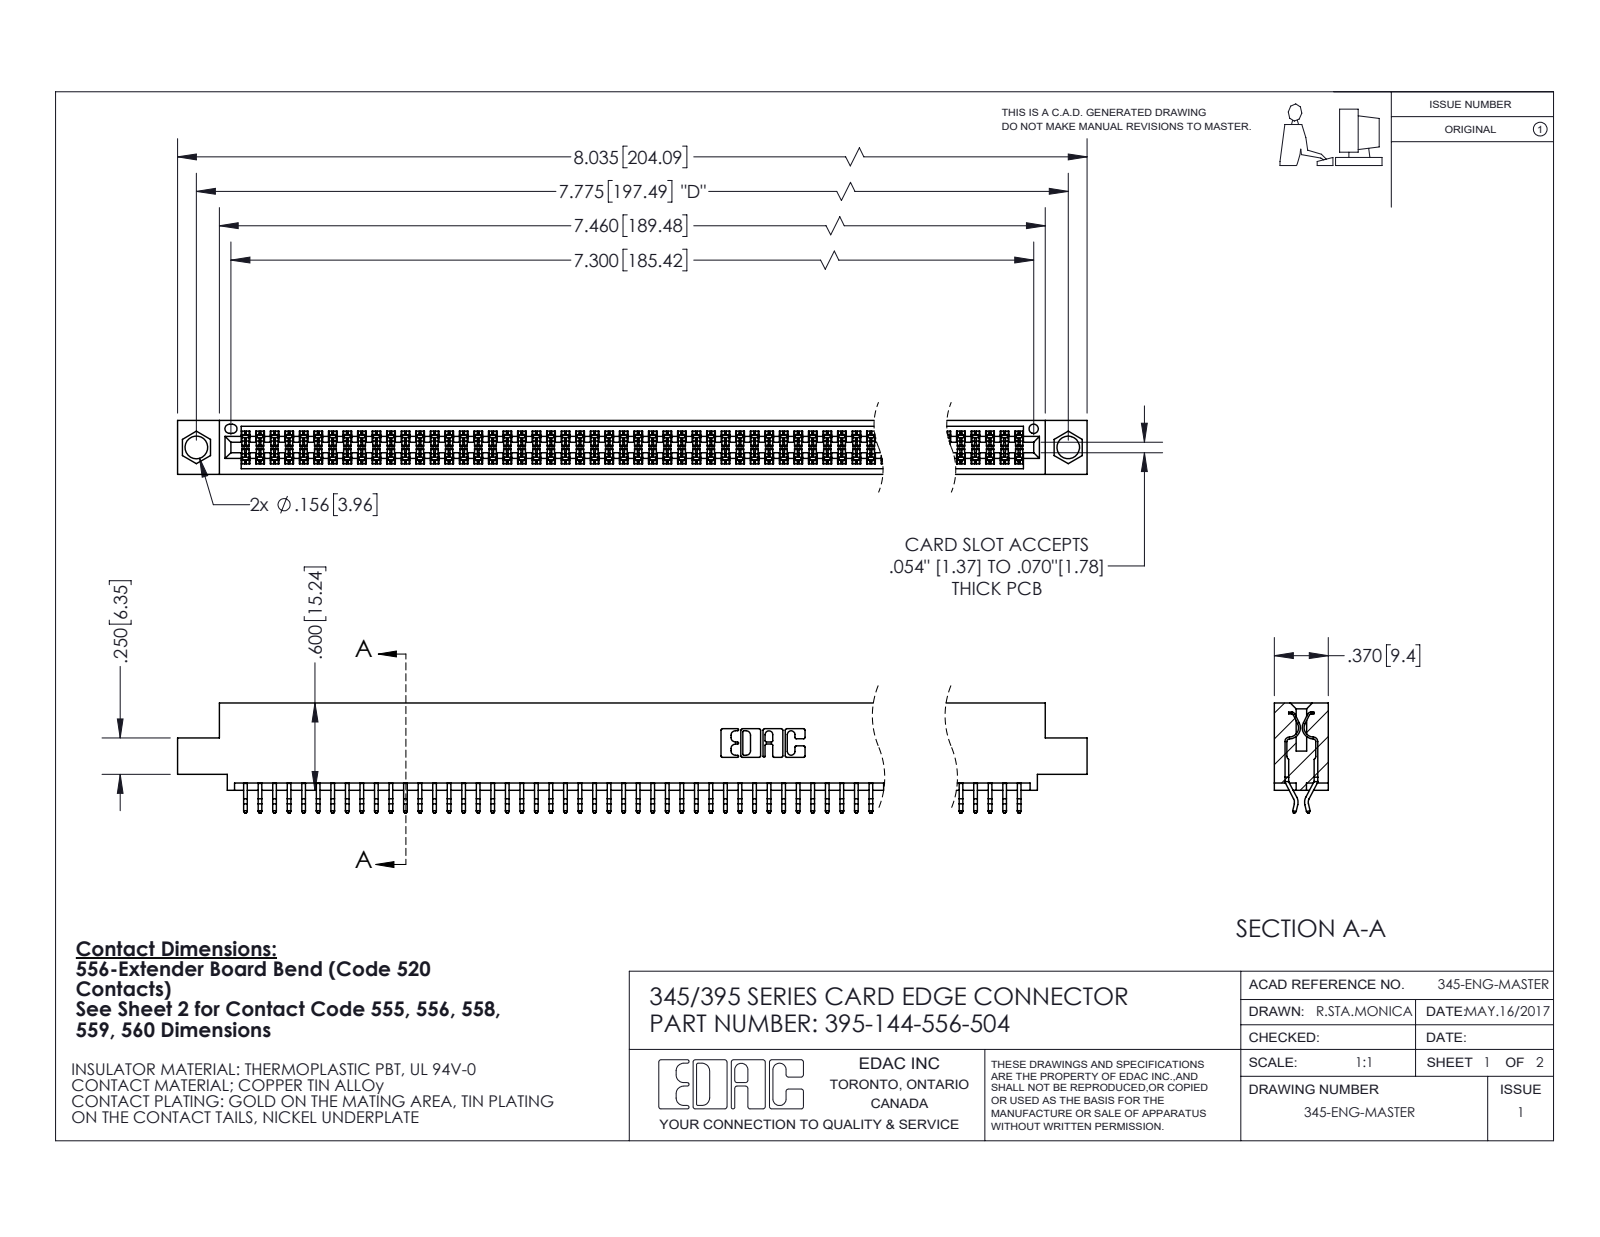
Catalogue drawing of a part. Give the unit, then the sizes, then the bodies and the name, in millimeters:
Units: millimetres
Overall size (bounding box): 204.1 × 19.2 × 9.4
Round holes (diameter × count): ⌀4 ×2, ⌀1.6 ×1
Partial cylindrical surfaces — rounded edges, fillets, slot ends (radius × count): R0.2 ×288, R0.3 ×22, R0.2 ×6, R0.8 ×6, R0.7 ×3, R0.3 ×2, R0.4 ×2, R0.5 ×2
Main face-to-face distances: 7.6, 1.8, 9.4, 5.1, 0.6, 2.5, 6.9, 5.7, 4.4, 3.8
Hole centre spacings: 6.9, 191.5, 197.5
Volume: 19 930 mm³ · Surface area: 29 850 mm²
Bodies: 145 solids, 8208 faces (5426 planar, 2782 cylindrical, 0 other)
Part name (STEP PRODUCT): 395-144-556-504; 345 Part_0.110 Offset - 0.156 Dia-TI; 345-292-001_556 Tail
STEP written by: SolidWorks 2020 (CONFIG_CONTROL_DESIGN)
